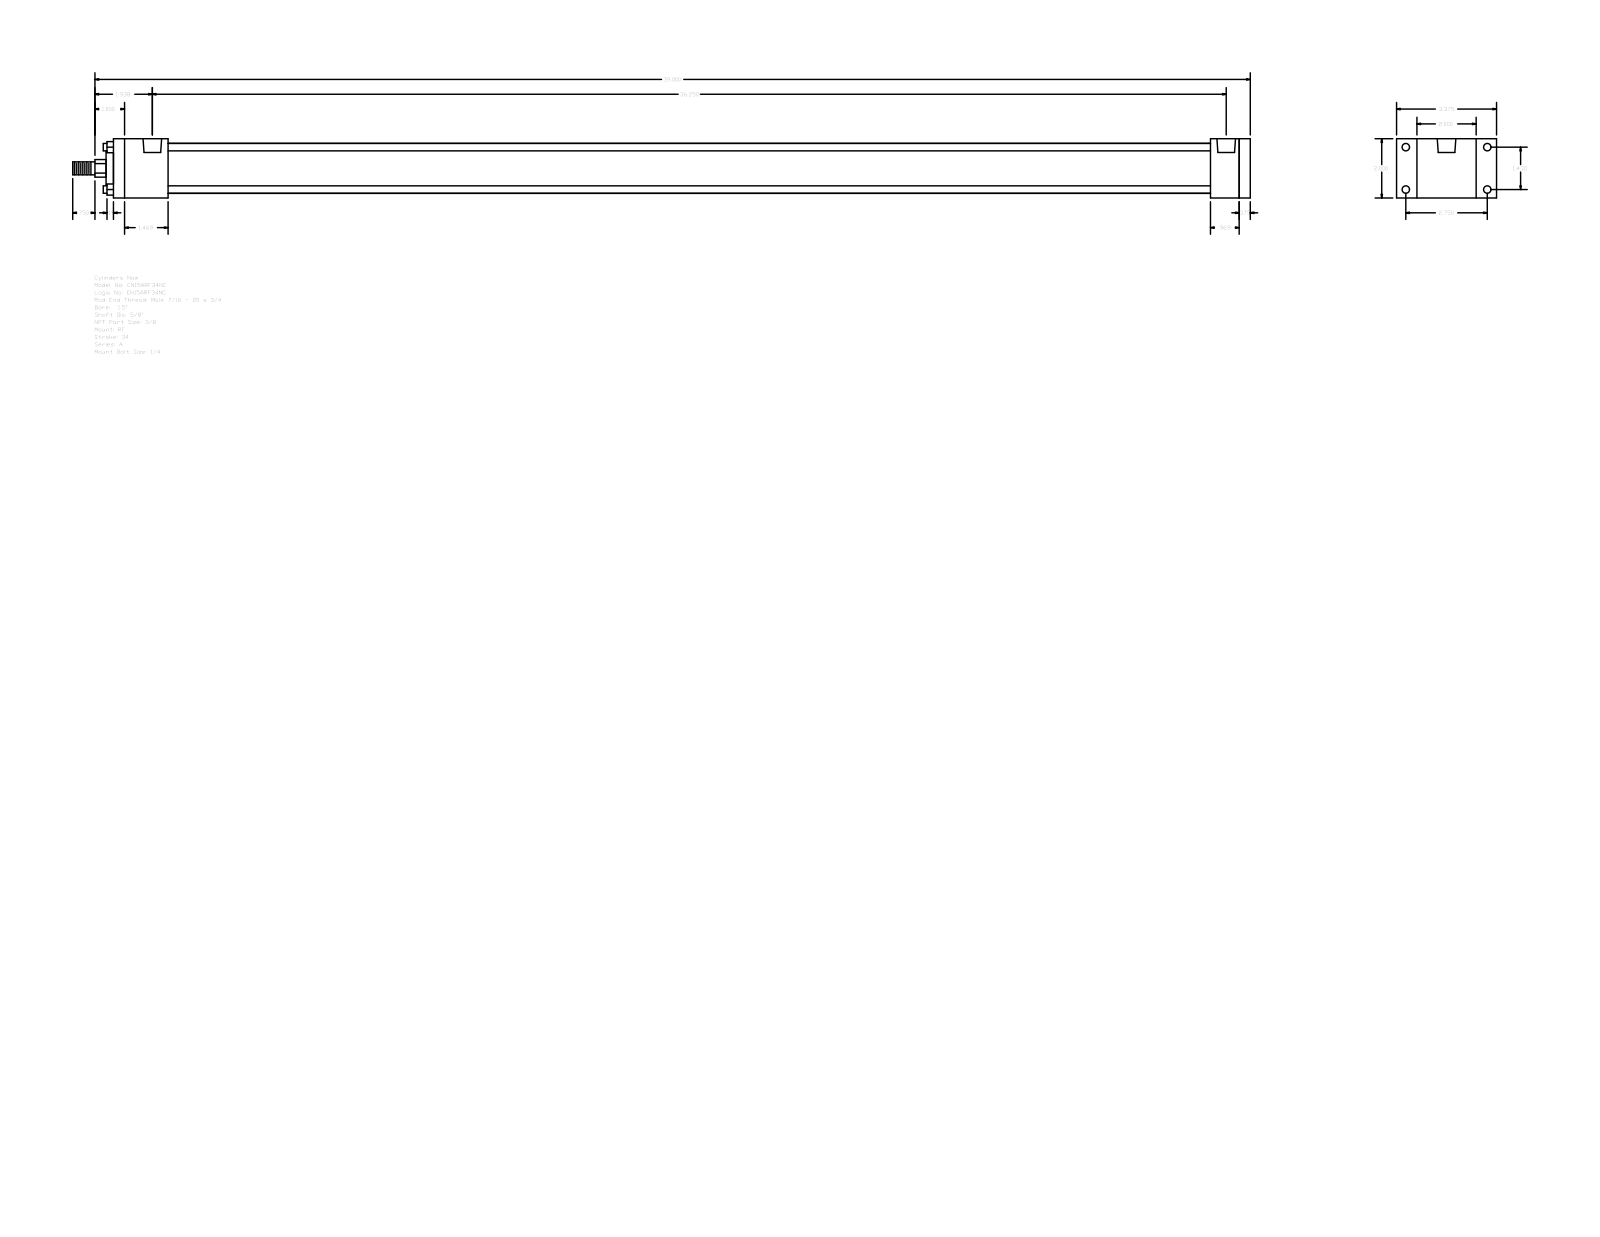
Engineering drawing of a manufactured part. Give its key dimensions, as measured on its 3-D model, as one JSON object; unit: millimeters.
{"part_name": "A_RF__0150_0.625", "step_written_by": "GSSL Pune (CONFIG_CONTROL_DESIGN)", "units": "millimeters", "bodies": {"solids": 0, "faces": 92, "planar": 64, "cylindrical": 28, "other": 0}, "overall_size": [1009.65, 85.72, 50.8], "round_holes": [[5.56, 4], [6.35, 4], [15.93, 2]], "round_bosses_or_shafts": [[6.35, 4], [42.93, 1], [28.57, 1], [15.88, 1], [11.11, 1]], "partial_cylinders_radius": [[7.54, 1]], "face_to_face_distances": [50.8, 9.52, 965.2, 974.72, 940.59, 24.61, 34.13, 46.83, 893.76, 918.37], "hole_center_spacings": [3.97, 36.32, 69.84, 78.72, 912.81, 916.78, 920.75]}
